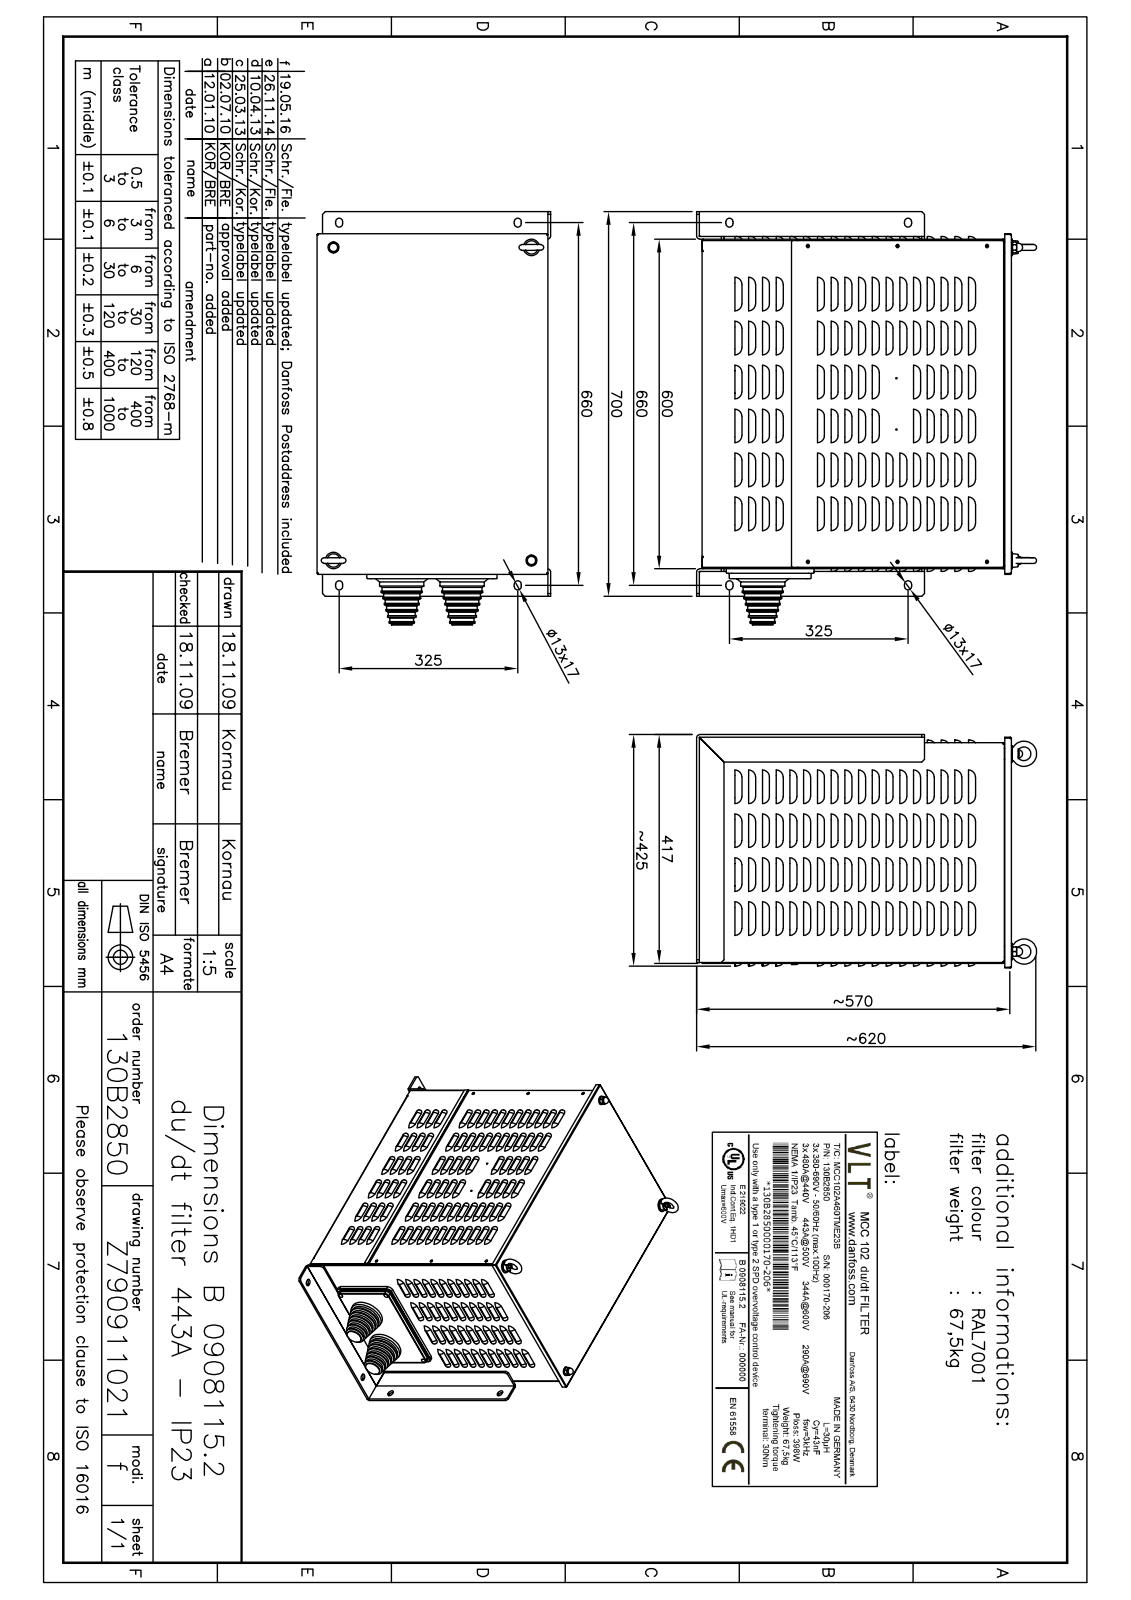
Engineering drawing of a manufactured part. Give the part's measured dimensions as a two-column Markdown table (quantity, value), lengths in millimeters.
| quantity | value |
| --- | --- |
| part name | pan head cross recess screw_din_ISO 7045 - M4 x 8 - Z --- 8N; #143-0135; Plain Washer Grade A_DIN_Washer DIN 125 - A 10.5; Frontwand oben #020-1794_Mit Kiemen (+8 more) |
| STEP written by | SolidWorks 2014 (AUTOMOTIVE_DESIGN) |
| units | millimeters |
| bodies | 133 solids, 5918 faces (2841 planar, 1263 cylindrical, 1814 other) |
| overall size | 752.5 × 615.2 × 425 |
| volume | 11 010 000 mm³ |
| surface area | 5 757 000 mm² |
| round holes (diameter × count) | 11 × 10, 2 × 6, 3.7 × 6, 6.8 × 6, 8 × 6, 8.4 × 6, 13 × 6, 4.1 × 5, 2.5 × 4, 4.5 × 4, 5.5 × 4, 6 × 4 |
| round bosses / shafts (diameter × count) | 16 × 6, 13 × 6, 8 × 6, 7.6 × 5, 20 × 4, 9 × 3, 6 × 3, 4 × 3 |
| partial cylindrical surfaces (radius × count) | 12 × 63, 13.5 × 63, 0.1 × 37, 1 × 32, 5.5 × 24, 1.6 × 22, 6.5 × 16, 0.74 × 12 |
| main face-to-face distances | 1.5, 556.2, 400, 598.5, 398.5, 557.7, 401.5, 554.7, 3, 5 |
| hole center spacings | 88, 29.26, 62.31, 176, 82.71, 94.34, 99.33, 101.79 |
